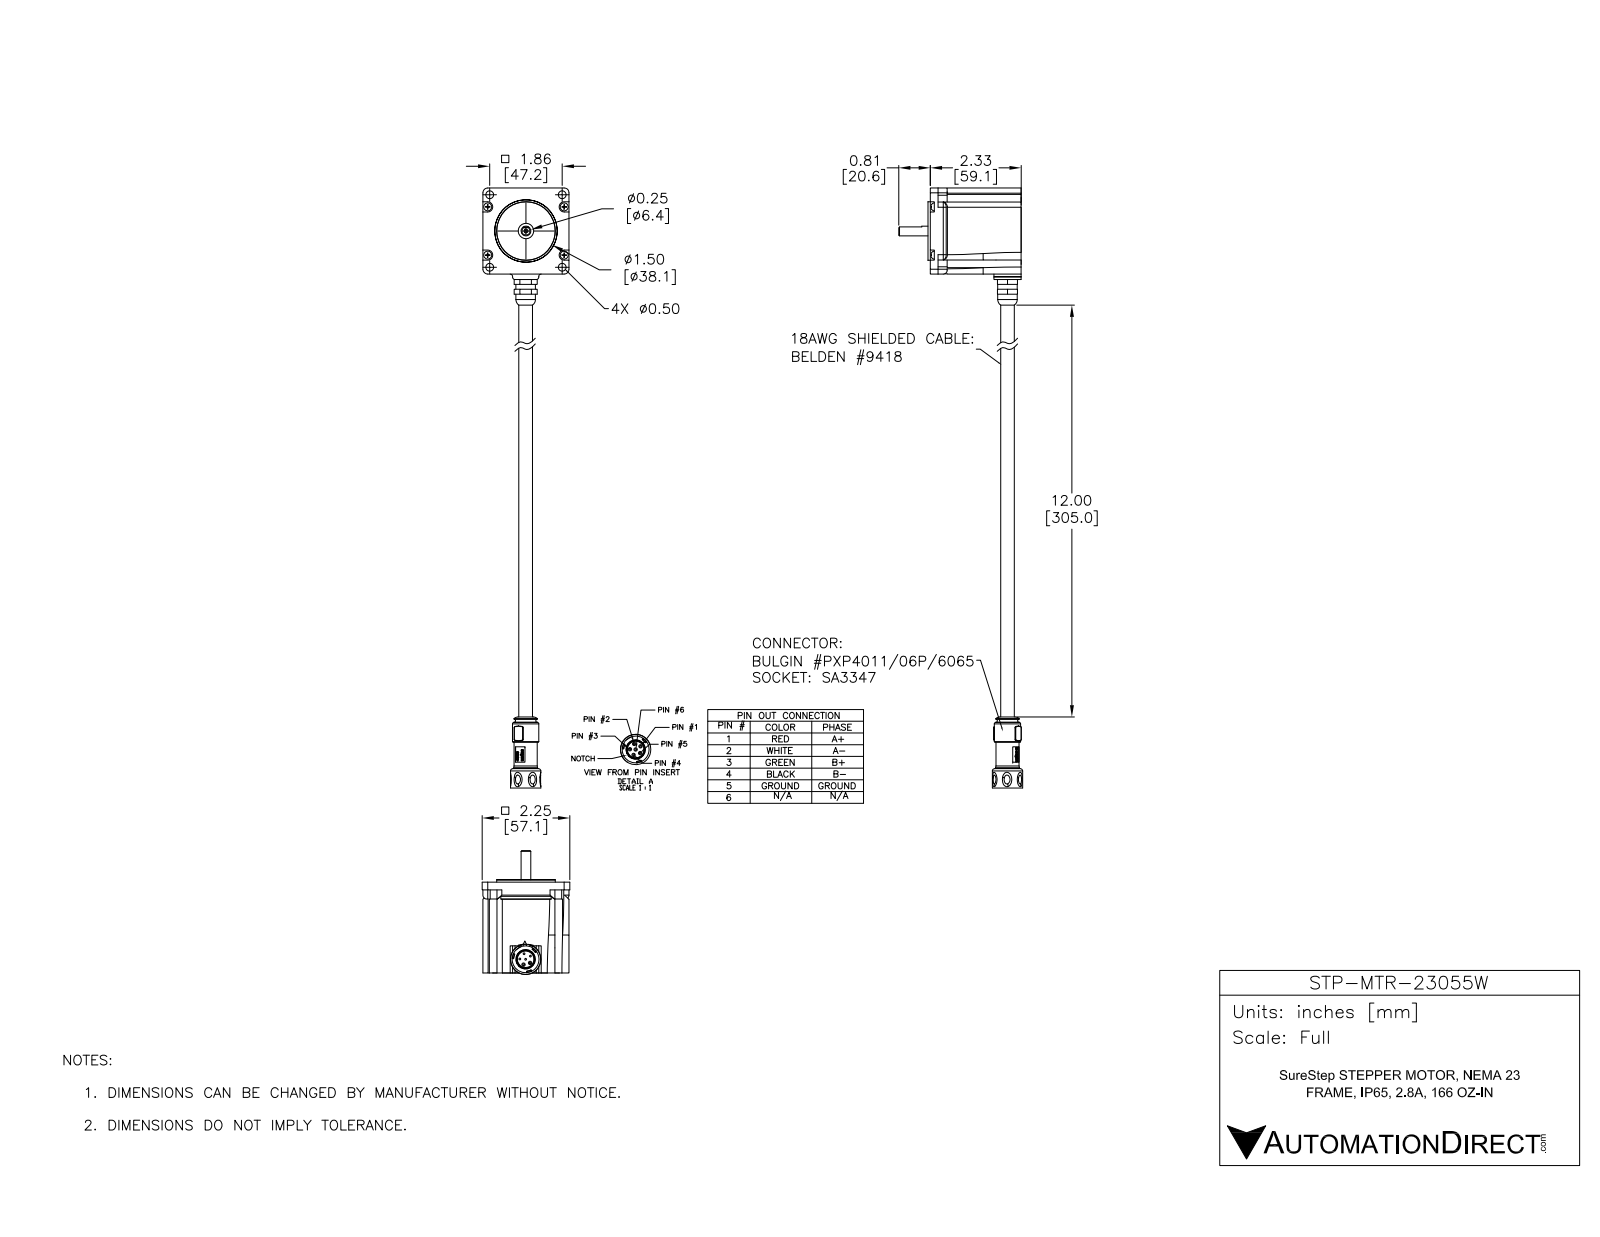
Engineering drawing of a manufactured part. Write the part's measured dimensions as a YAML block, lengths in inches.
part_name: "STP-MTR-23055W"
step_written_by: "SolidWorks 2017 (AUTOMOTIVE_DESIGN)"
units: inches
bodies: {solids: 3, faces: 902, planar: 367, cylindrical: 234, other: 301}
overall_size: [15.376, 3.176, 2.207]
volume: 10.82
surface_area: 65.33
round_holes:
  - {diameter: 0.047, count: 6}
  - {diameter: 0.097, count: 4}
  - {diameter: 0.2, count: 4}
  - {diameter: 0.125, count: 3}
  - {diameter: 0.125, count: 2}
  - {diameter: 0.063, count: 1}
  - {diameter: 0.228, count: 1}
  - {diameter: 0.394, count: 1}
  - {diameter: 0.398, count: 1}
  - {diameter: 0.449, count: 1}
  - {diameter: 0.467, count: 1}
  - {diameter: 0.689, count: 1}
round_bosses_or_shafts:
  - {diameter: 0.05, count: 4}
  - {diameter: 1.7, count: 1}
  - {diameter: 1.5, count: 1}
  - {diameter: 0.777, count: 1}
  - {diameter: 0.674, count: 1}
  - {diameter: 0.613, count: 1}
  - {diameter: 0.592, count: 1}
  - {diameter: 0.5, count: 1}
partial_cylinders:
  - {radius: 0.005, count: 28}
  - {radius: 0.02, count: 12}
  - {radius: 0.125, count: 10}
  - {radius: 0.388, count: 6}
  - {radius: 0.062, count: 4}
  - {radius: 0.129, count: 4}
  - {radius: 0.175, count: 4}
  - {radius: 0.196, count: 4}
face_to_face_distances: [2.207, 0.314, 2.014, 1.7, 0.311, 0.624, 2.324, 0.313, 0.627, 2.327]
hole_center_spacings: [0.148, 0.174, 0.316, 1.181, 1.553, 1.649, 1.661, 2.478]
